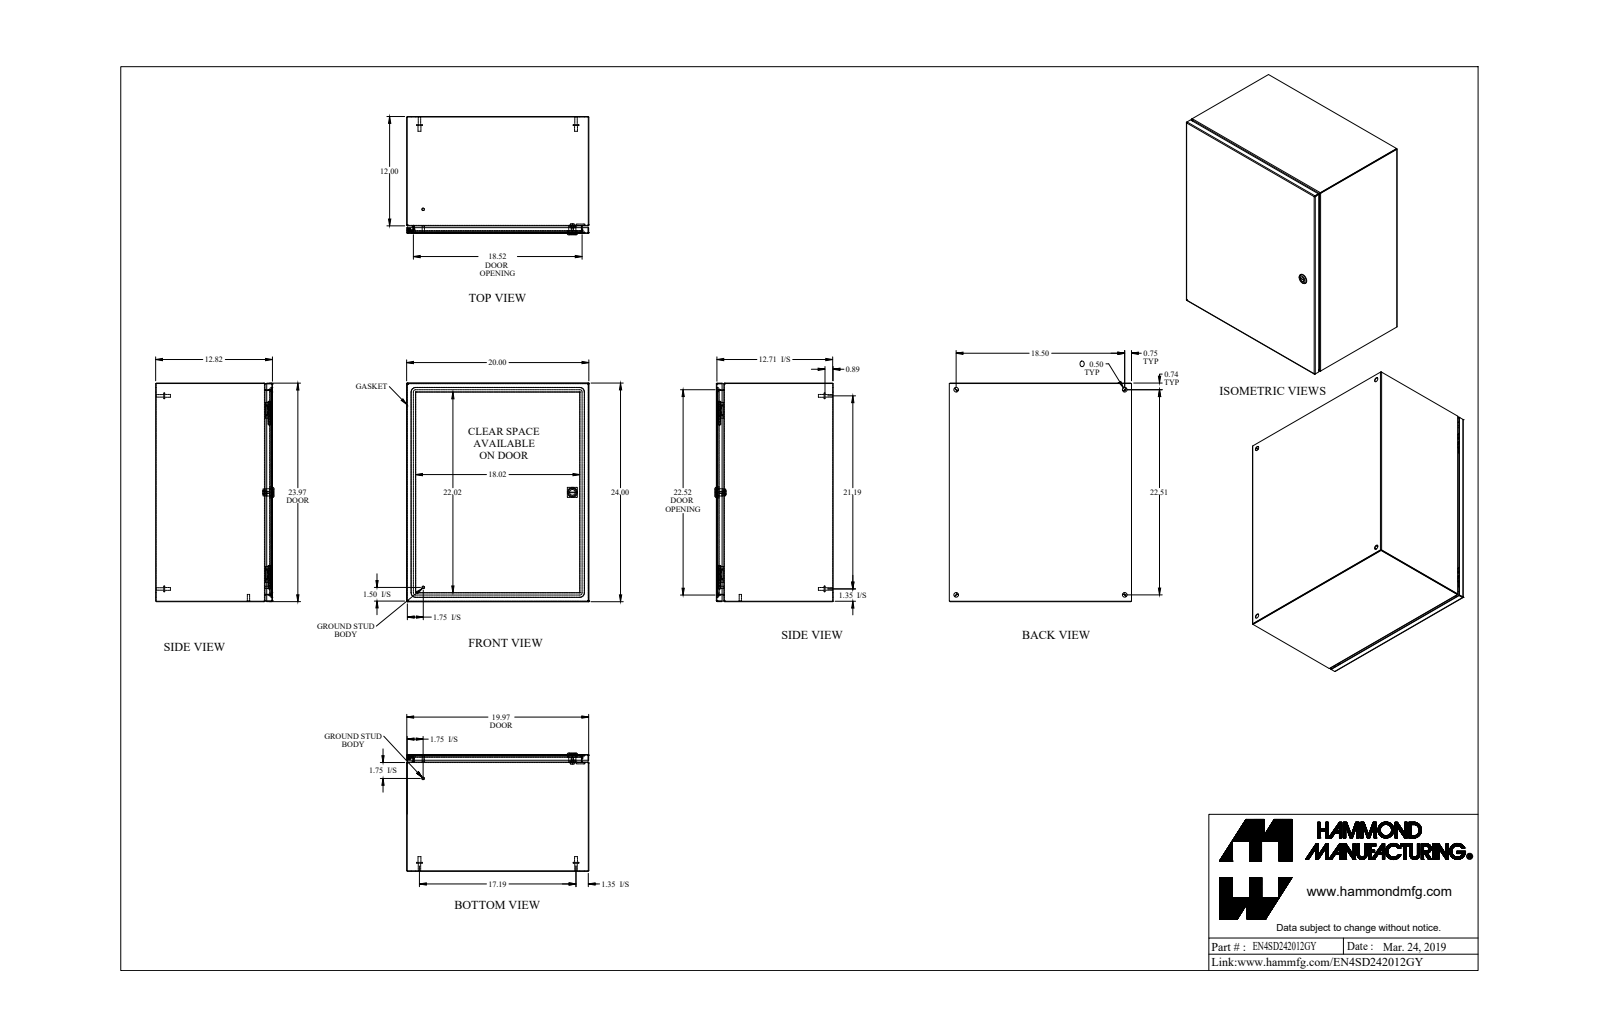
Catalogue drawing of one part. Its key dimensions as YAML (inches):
part_name: "EN4SD242012GY_Default"
step_written_by: "SolidWorks 2019 (CONFIG_CONTROL_DESIGN)"
units: inches
bodies: {solids: 23, faces: 622, planar: 293, cylindrical: 201, other: 128}
overall_size: [24, 20, 12.982]
volume: 133.1
surface_area: 4569
round_holes:
  - {diameter: 0.5, count: 4}
  - {diameter: 0.172, count: 1}
  - {diameter: 0.232, count: 1}
  - {diameter: 0.24, count: 1}
  - {diameter: 0.242, count: 1}
  - {diameter: 0.625, count: 1}
  - {diameter: 0.785, count: 1}
round_bosses_or_shafts:
  - {diameter: 0.625, count: 4}
  - {diameter: 0.313, count: 4}
  - {diameter: 0.27, count: 4}
  - {diameter: 0.281, count: 2}
  - {diameter: 0.25, count: 2}
  - {diameter: 1.1, count: 1}
  - {diameter: 0.525, count: 1}
  - {diameter: 0.455, count: 1}
partial_cylinders:
  - {radius: 0.029, count: 19}
  - {radius: 0.086, count: 19}
  - {radius: 0.188, count: 12}
  - {radius: 0.006, count: 4}
  - {radius: 0.062, count: 4}
  - {radius: 0.25, count: 4}
  - {radius: 0.499, count: 4}
  - {radius: 0.125, count: 2}
face_to_face_distances: [0.057, 12.765, 19.943, 12.708, 23.943, 12.822, 19.886, 20, 23.886, 24]
hole_center_spacings: [18.5, 22.514, 29.14, 11.298, 11.315, 20.755, 20.764]
